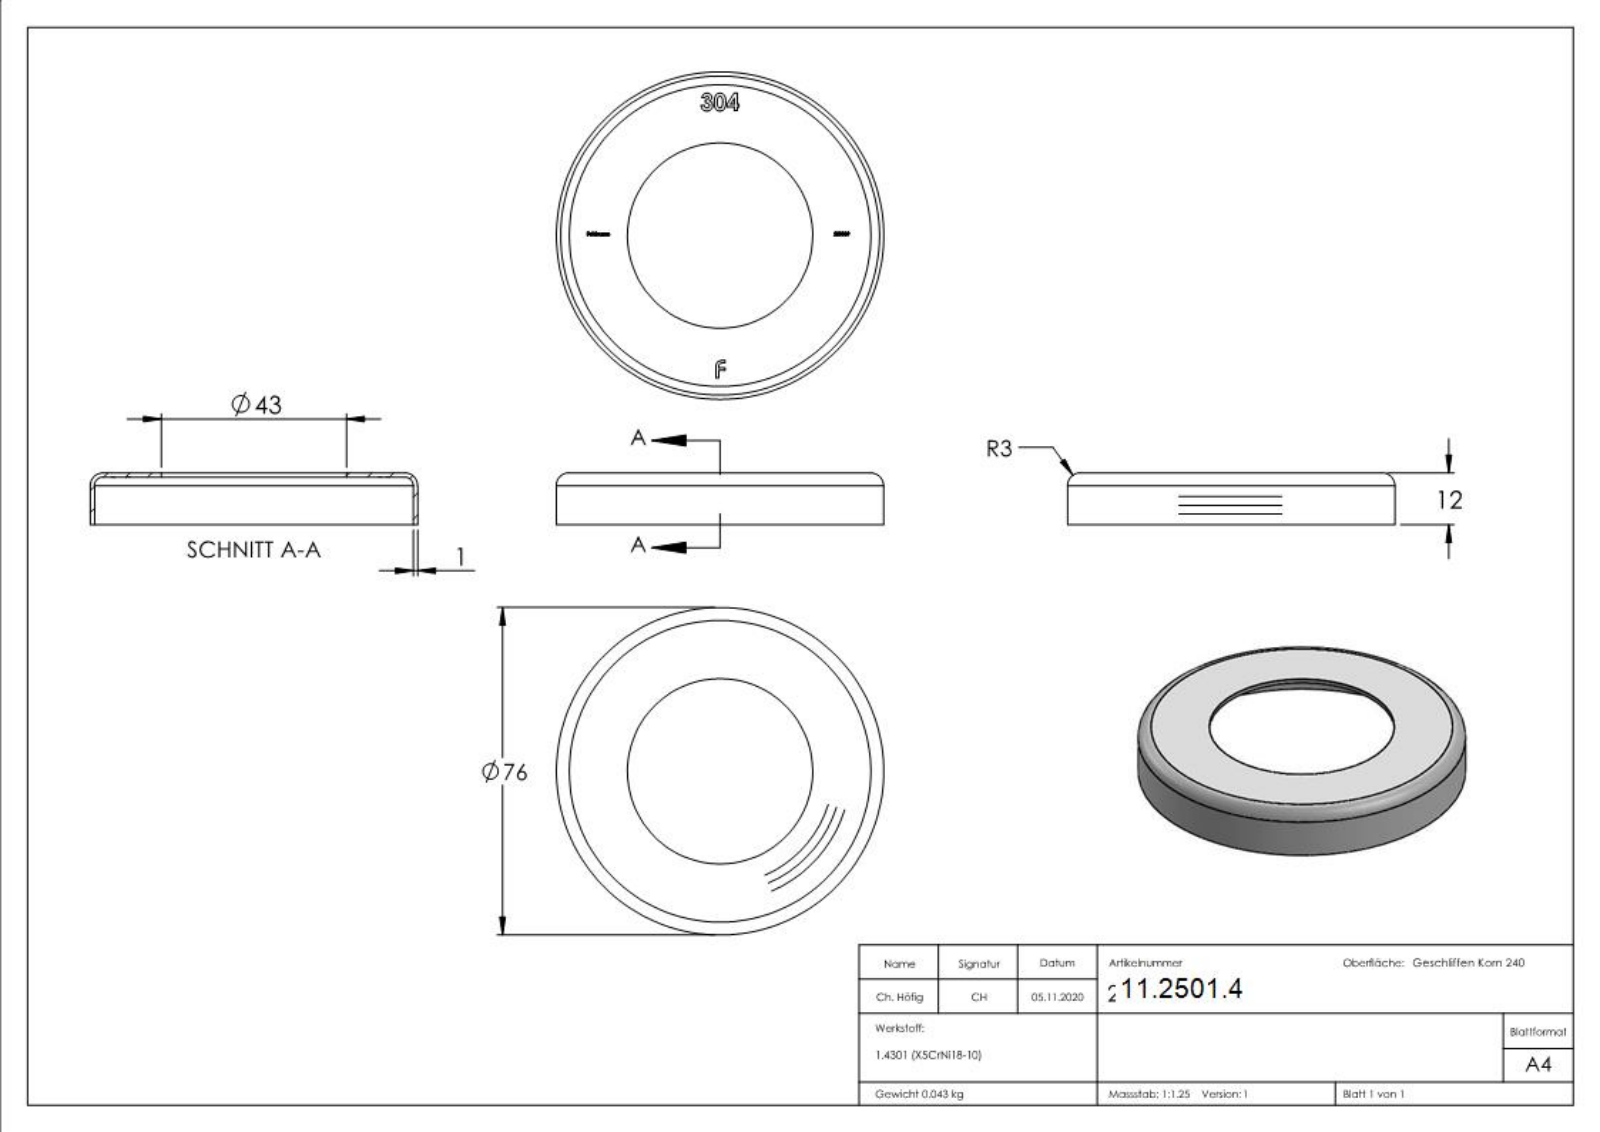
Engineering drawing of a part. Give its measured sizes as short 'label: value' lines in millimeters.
name: 200039
written by: SolidWorks 2018 (CONFIG_CONTROL_DESIGN)
unit: mm
bodies: 1 solid, 262 faces (123 planar, 6 cylindrical, 133 other)
size: 76 × 76 × 12
volume: 5 418 mm³; area: 11 225 mm²
holes: 1× ⌀43, 1× ⌀74
bosses: 1× ⌀76
face distances: 1, 11, 12, 11.1, 0.9, 0.71, 5, 0.58, 1.78, 4.29
